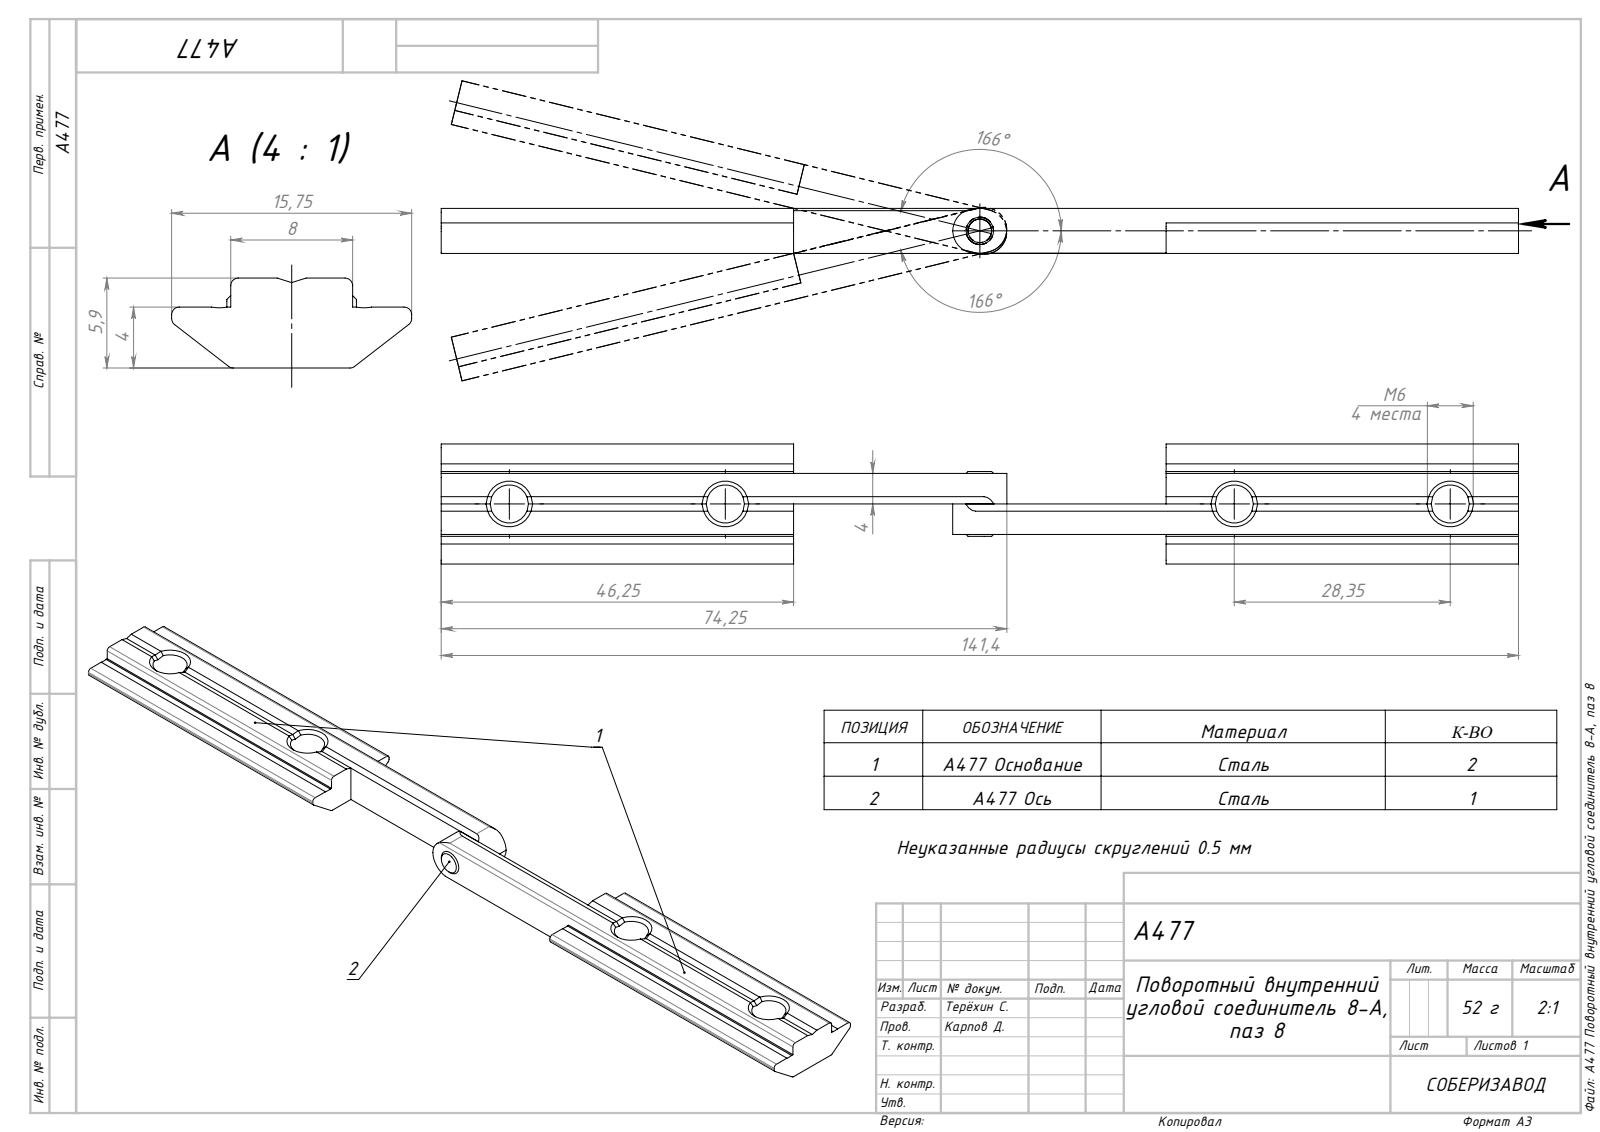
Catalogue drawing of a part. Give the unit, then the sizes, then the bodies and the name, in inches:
Units: inches
Overall size (bounding box): 5.567 × 0.62 × 0.232
Round holes (diameter × count): ⌀0.197 ×4, ⌀0.118 ×1
Partial cylindrical surfaces — rounded edges, fillets, slot ends (radius × count): R0.02 ×12, R0.118 ×4, R0.099 ×2
Main face-to-face distances: 0.157, 0.232, 0.075, 0.315, 1.821, 3.746, 5.567, 1.925, 0.152, 0.31
Hole centre spacings: 1.116, 3.746, 2.63, 4.862
Volume: 0.422 in³ · Surface area: 8.06 in²
Bodies: 3 solids, 128 faces (50 planar, 38 cylindrical, 40 other)
Part name (STEP PRODUCT): A476 Основание_00; A476 Ось_00; A476 Поворотный внутренний угловой соединитель 8-B, паз 8
STEP written by: SolidWorks 2021 (AUTOMOTIVE_DESIGN)
